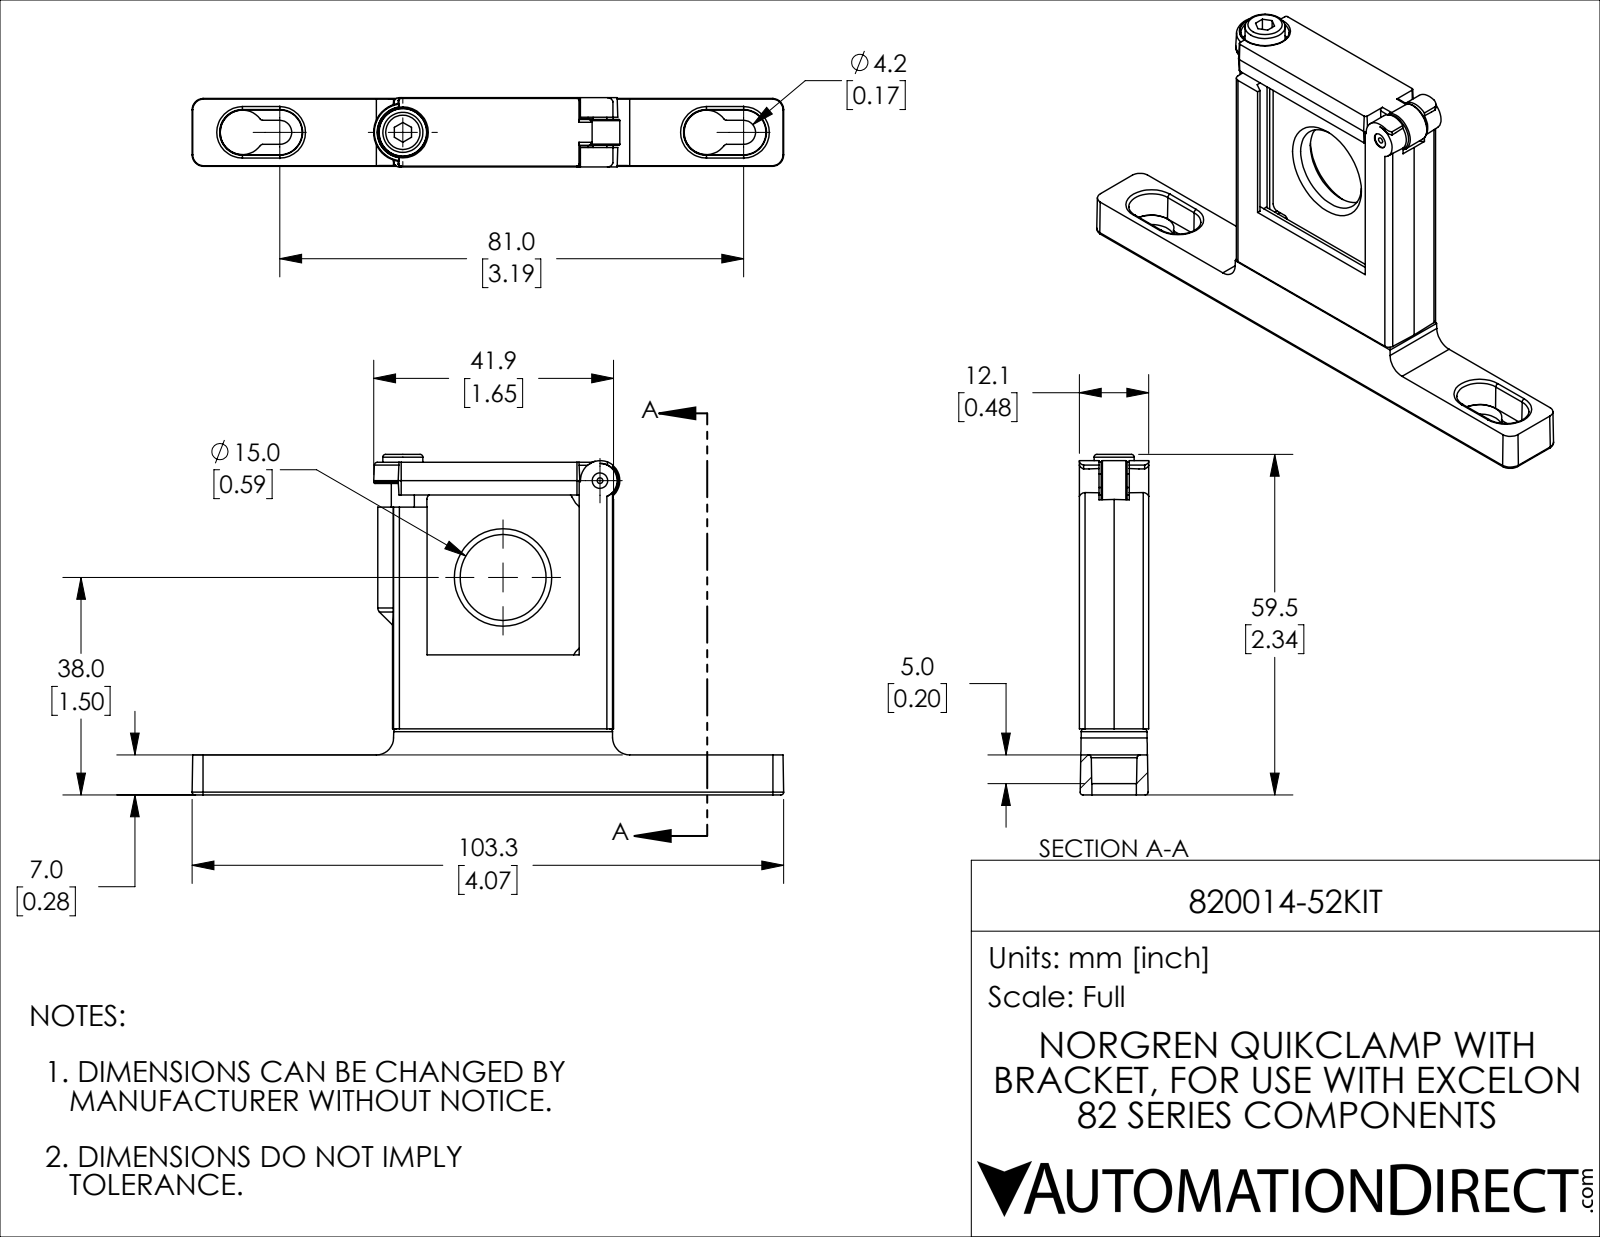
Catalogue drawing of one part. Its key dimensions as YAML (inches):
part_name: "820014-52KIT"
step_written_by: "SolidWorks 2021 (CONFIG_CONTROL_DESIGN)"
units: inches
bodies: {solids: 1, faces: 348, planar: 162, cylindrical: 111, other: 75}
overall_size: [4.066, 2.341, 0.476]
volume: 1.112
surface_area: 22.83
round_holes:
  - {diameter: 0.306, count: 2}
  - {diameter: 0.039, count: 1}
  - {diameter: 0.106, count: 1}
  - {diameter: 0.128, count: 1}
  - {diameter: 0.175, count: 1}
  - {diameter: 0.187, count: 1}
  - {diameter: 0.591, count: 1}
round_bosses_or_shafts:
  - {diameter: 0.276, count: 2}
  - {diameter: 0.274, count: 1}
  - {diameter: 0.157, count: 1}
  - {diameter: 0.094, count: 1}
partial_cylinders:
  - {radius: 0.039, count: 30}
  - {radius: 0.02, count: 20}
  - {radius: 0.03, count: 6}
  - {radius: 0.118, count: 3}
  - {radius: 0.083, count: 2}
  - {radius: 0.175, count: 2}
  - {radius: 0.197, count: 2}
  - {radius: 0.232, count: 2}
face_to_face_distances: [0.152, 0.325, 0.476, 0.071, 0.406, 0.081, 0.254, 0.173, 0.079, 0.179]
hole_center_spacings: [0.689, 0.941, 1.102, 1.398, 1.791, 2.087, 3.189]
